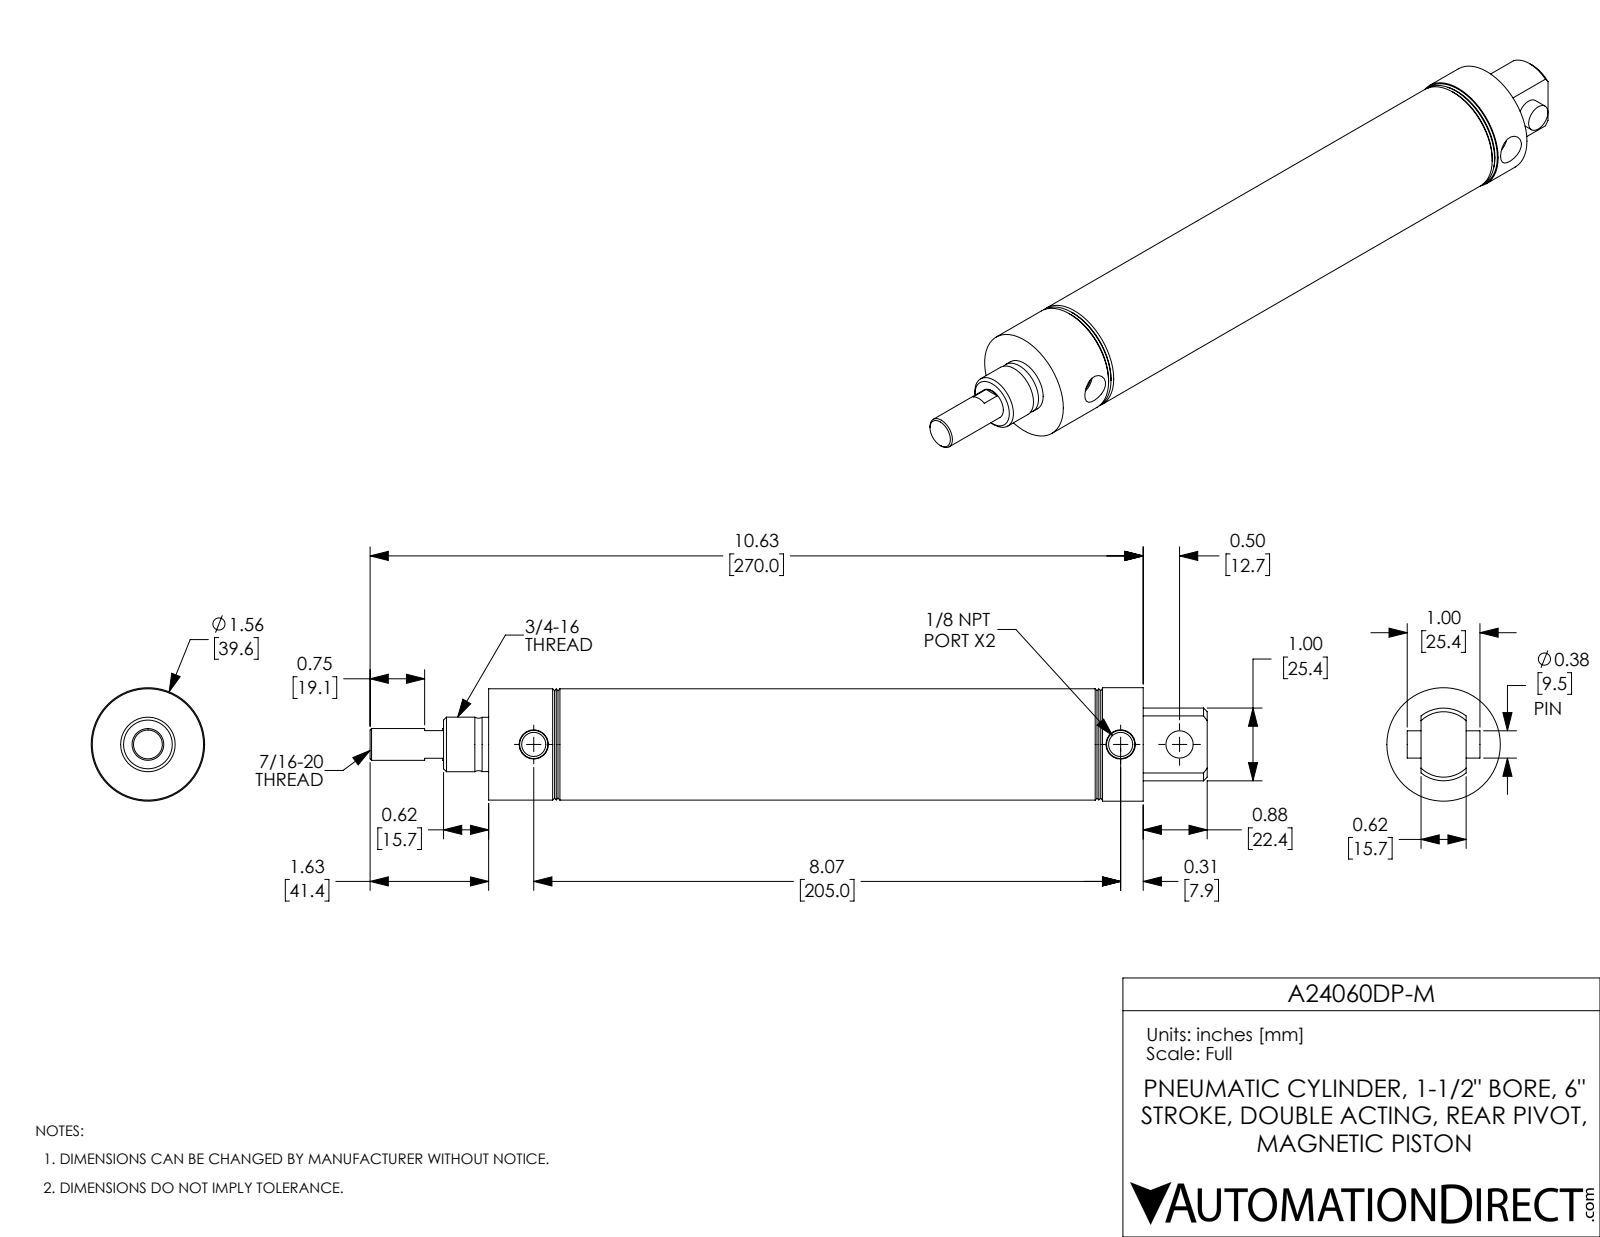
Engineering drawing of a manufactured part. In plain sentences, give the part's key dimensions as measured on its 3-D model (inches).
The part is named "A24060DP-M-Rod; A24060DP-M-MainBody; A24060DP-M-Pin; A24060DP-M". Its 3-D file was written by "SolidWorks 2017 (AUTOMOTIVE_DESIGN)". It is 3 solids with 84 faces: 22 planar, 28 cylindrical and 34 other. Overall it measures 11.51 by 1.56 by 1.56 inches. Its volume is 7.737 cubic inches and its surface area 108.8 square inches. Round holes: 2 of diameter 0.332, 1 of diameter 0.375, 1 of diameter 0.437, 1 of diameter 1.5. Round bosses or shafts: 1 of diameter 1.56, 1 of diameter 1.53, 1 of diameter 0.75, 1 of diameter 0.746. Partial cylindrical surfaces (rounded edges, fillets, slot ends): 1 of radius 0.5. The main face-to-face distances are 1.25, 7.75, 6.5, 0.5, 6, 7.25, 1.75, 9, 0.62, 0.88. The hole center spacings are 0.81, 8.07, 8.88.
